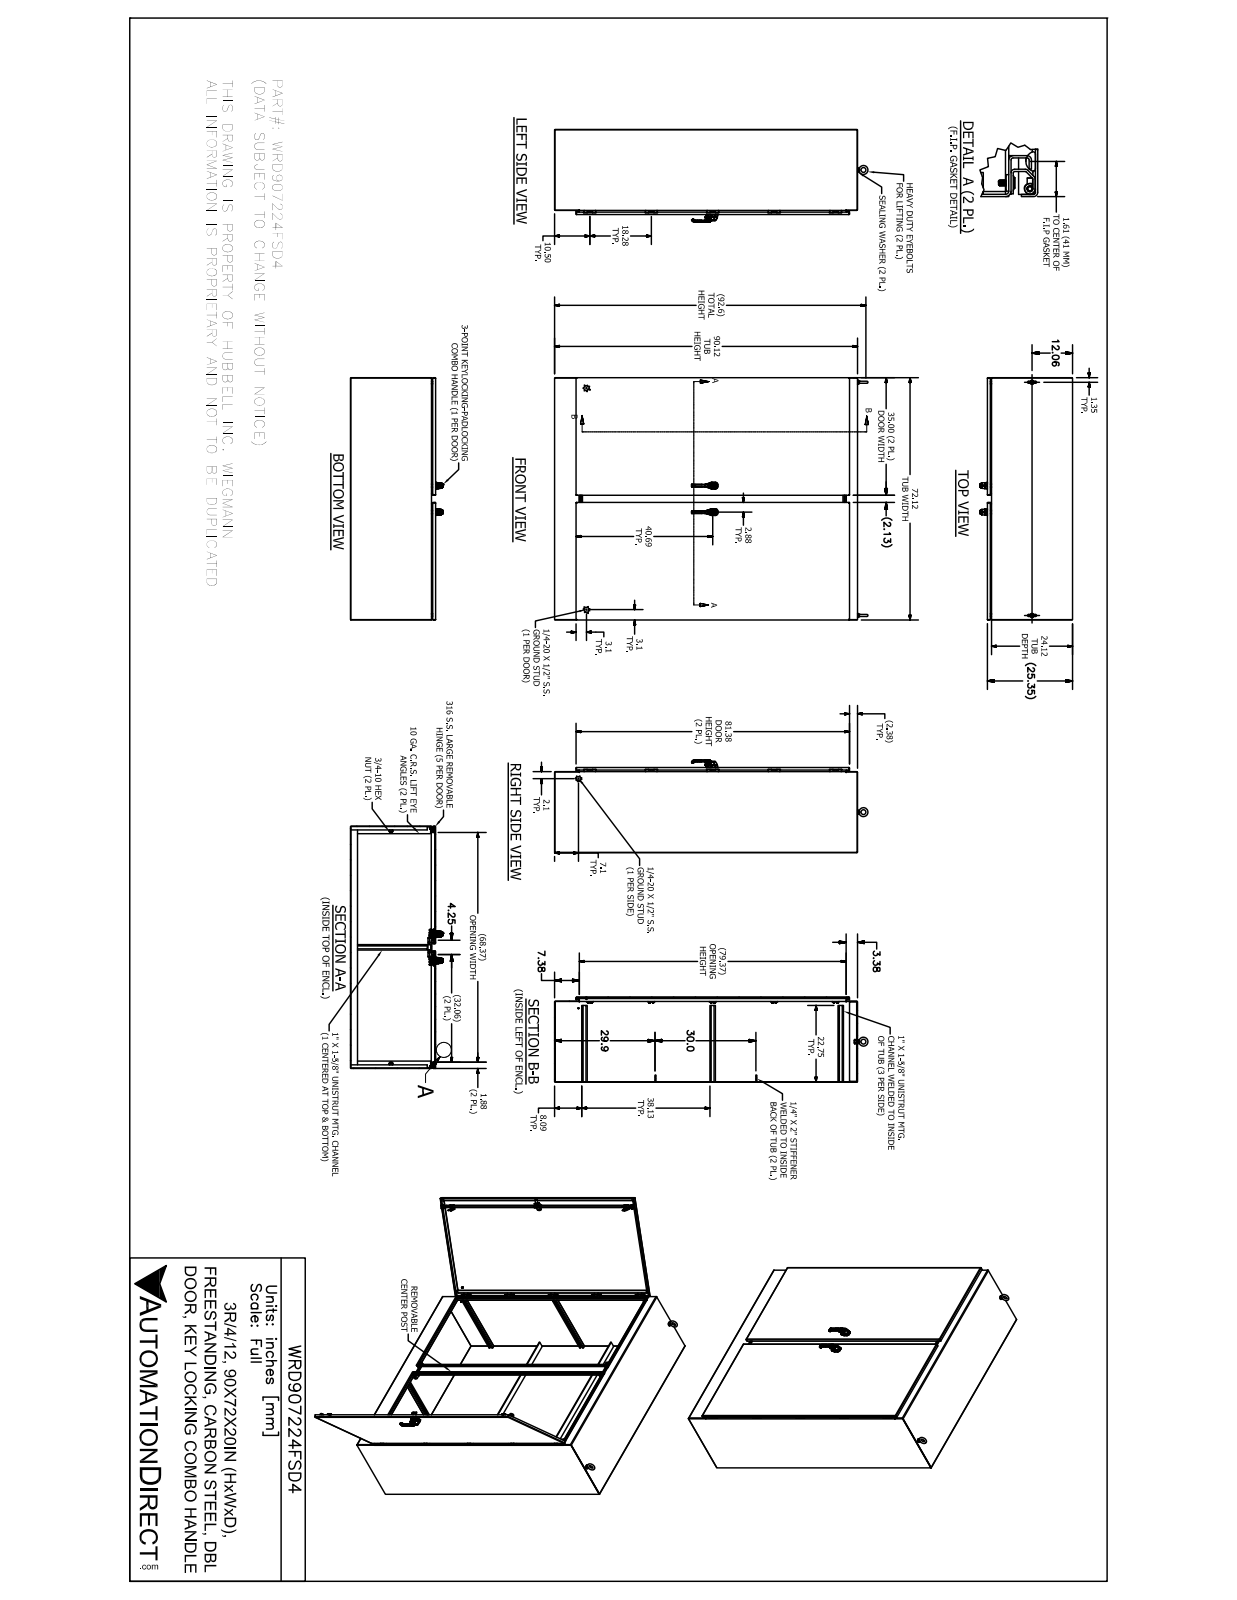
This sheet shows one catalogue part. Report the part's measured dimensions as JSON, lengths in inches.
{"part_name": "WRD907224FSD4", "step_written_by": "SolidWorks 2017 (AUTOMOTIVE_DESIGN)", "units": "inches", "bodies": {"solids": 170, "faces": 3566, "planar": 1652, "cylindrical": 1192, "other": 722}, "overall_size": [93.248, 72.133, 27.527], "volume_in3": 2724, "surface_area_in2": 49939, "round_holes": [[0.266, 24], [0.23, 20], [0.281, 20], [0.65, 20], [0.2, 8], [0.277, 8], [0.281, 6], [0.156, 4], [0.252, 4], [0.4, 4], [0.45, 4], [0.241, 3]], "round_bosses_or_shafts": [[0.625, 17], [0.25, 14], [0.533, 4], [0.438, 4], [0.375, 4], [0.313, 4], [0.213, 4], [1, 3]], "partial_cylinders_radius": [[0.062, 47], [0.125, 36], [0.05, 32], [0.063, 25], [0.01, 20], [0.019, 16], [0.025, 16], [0.053, 16]], "face_to_face_distances": [0.104, 25.245, 25.141, 25.349, 72.021, 90.021, 71.917, 72.125, 89.917, 90.125], "hole_center_spacings": [73.195, 18.281, 1, 70.875, 70.882, 36.563, 54.844, 72.952]}
